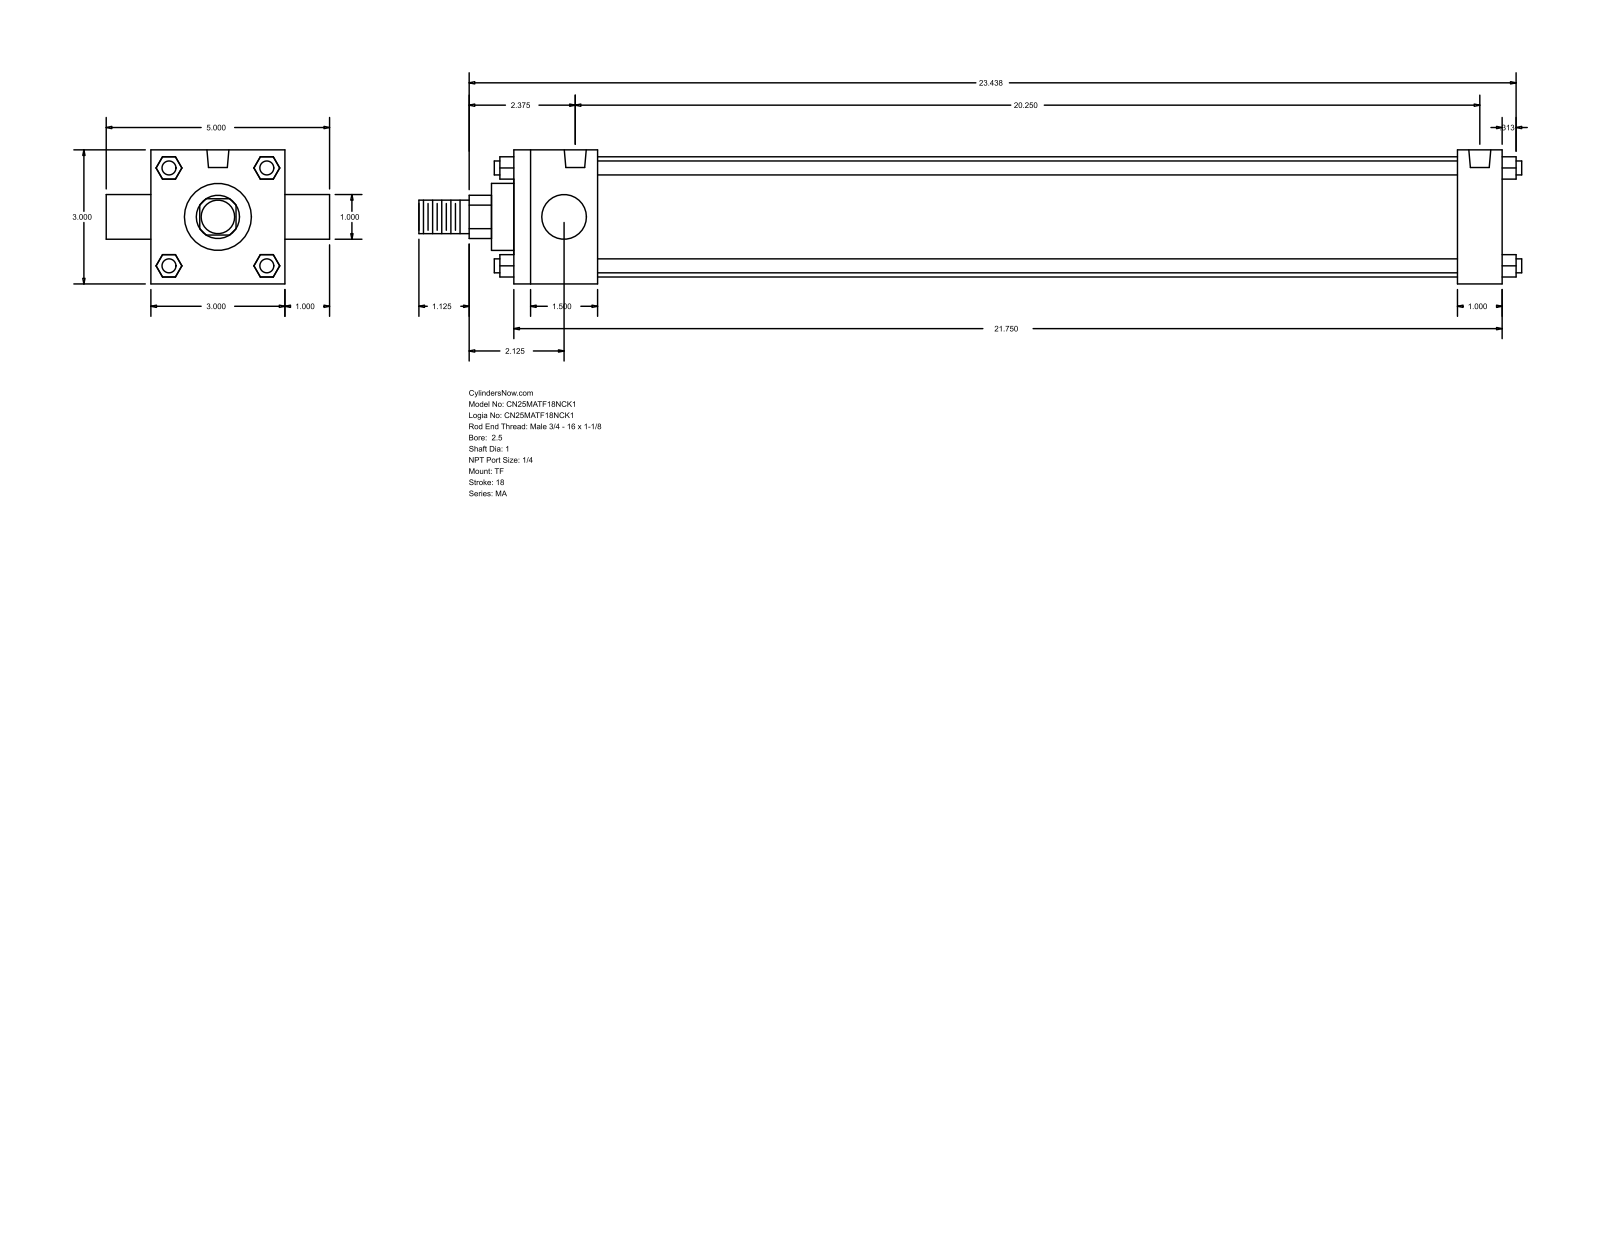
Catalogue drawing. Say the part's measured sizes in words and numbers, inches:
The part is named "MA_TF__0250_1". Its 3-D file was written by "GSSL Pune (CONFIG_CONTROL_DESIGN)". It is 0 solids with 120 faces: 92 planar, 28 cylindrical and 0 other. Overall it measures 24.687 by 5 by 3 inches. Round holes: 3 of diameter 0.313, 2 of diameter 0.492. Round bosses or shafts: 4 of diameter 0.313, 2 of diameter 1, 1 of diameter 2.69, 1 of diameter 1.5, 1 of diameter 0.75. Partial cylindrical surfaces (rounded edges, fillets, slot ends): 1 of radius 0.484. The main face-to-face distances are 3, 22.125, 1, 0.5, 1.875, 21.125, 19.25, 20.25, 4, 1.095. The hole center spacings are 20.25.
